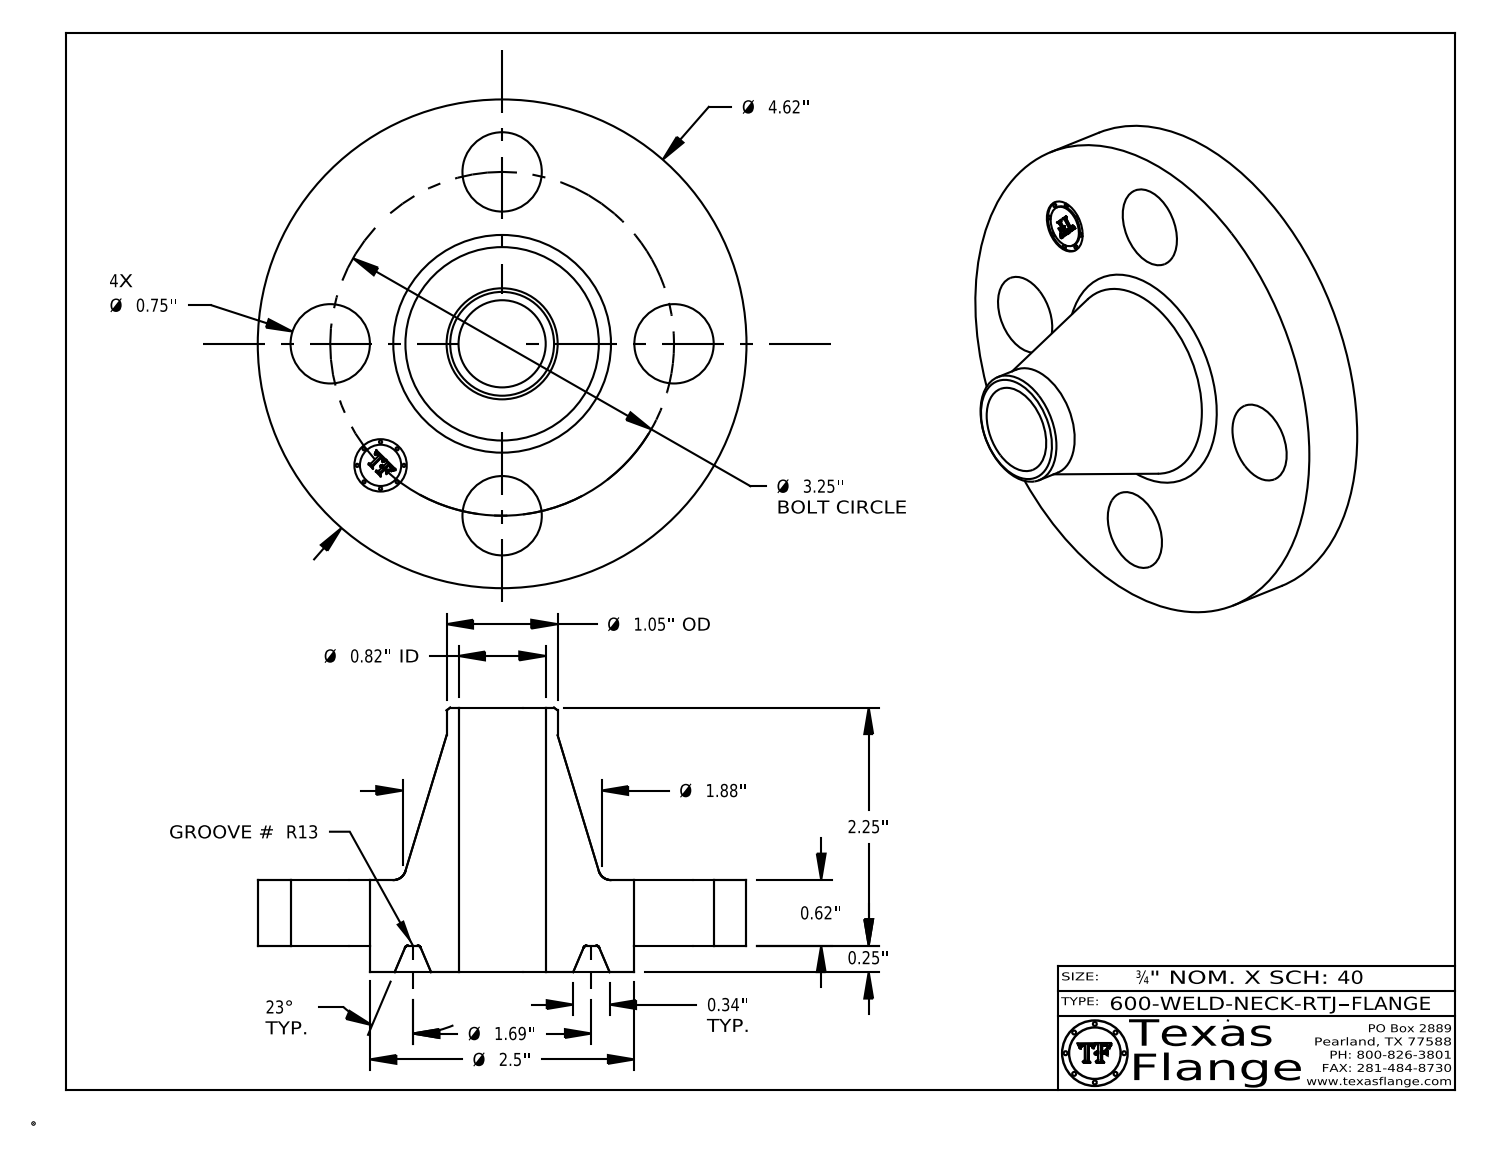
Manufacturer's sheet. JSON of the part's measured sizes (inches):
{"part_name": "600-WELD-NECK-RTJ", "step_written_by": "CATIA V5 STEP AP214 (AUTOMOTIVE_DESIGN)", "units": "inches", "bodies": {"solids": 1, "faces": 421, "planar": 371, "cylindrical": 36, "other": 14}, "overall_size": [4.62, 4.62, 2.5], "volume_in3": 11.48, "surface_area_in2": 59.33, "round_holes": [[0.75, 4], [0.495, 1], [0.824, 1]], "round_bosses_or_shafts": [[0.03, 8], [4.62, 1], [2.5, 1], [1.05, 1], [0.39, 1]], "face_to_face_distances": [0.62, 0.25, 0.87, 2.5, 2.25, 1.63, 0.855, 0.605, 0.015, 1.645], "hole_center_spacings": [1.625, 2.298, 1.244, 3.003, 3.25]}
